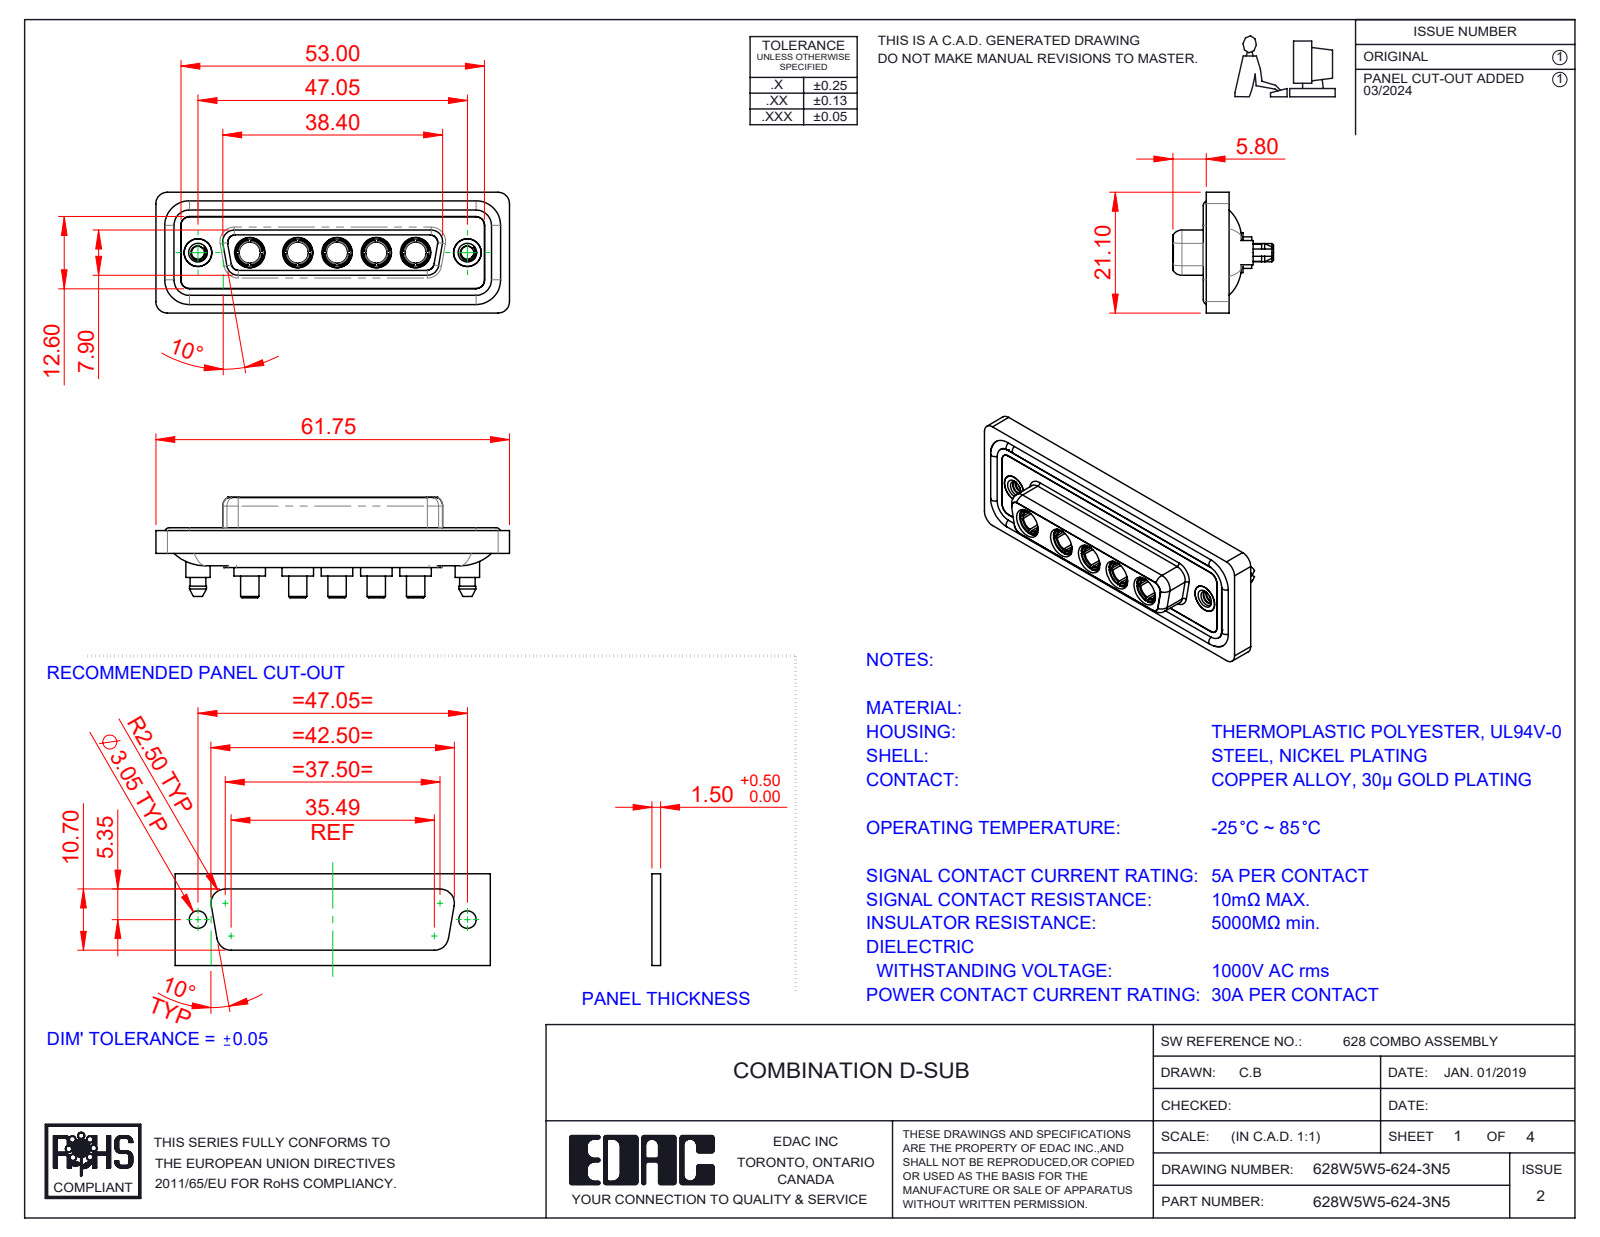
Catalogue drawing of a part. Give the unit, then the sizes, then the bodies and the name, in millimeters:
Units: millimetres
Overall size (bounding box): 61.75 × 21.1 × 17.55
Round holes (diameter × count): ⌀4.85 ×7, ⌀3.7 ×5, ⌀5.3 ×5, ⌀2.26 ×2, ⌀4 ×2, ⌀4.05 ×2, ⌀5 ×2
Round bosses / shafts (diameter × count): ⌀5.5 ×5, ⌀5.2 ×5, ⌀4.96 ×5, ⌀4.75 ×5, ⌀3.75 ×5, ⌀3.2 ×5, ⌀1.6 ×4, ⌀5.4 ×2
Partial cylindrical surfaces — rounded edges, fillets, slot ends (radius × count): R1.5 ×24, R2 ×18, R1.6 ×10, R1.35 ×8, R2.1 ×5, R0.25 ×4, R0.5 ×4, R0.6 ×4
Main face-to-face distances: 0.4, 1.8, 7.45, 5.65, 0.5, 7.05, 6.6, 1.6, 1.1, 2.9
Hole centre spacings: 6.86, 9.04, 13.72, 38.01, 8.39, 15.25, 15.9, 17.43
Volume: 8 342 mm³ · Surface area: 13 771 mm²
Bodies: 17 solids, 806 faces (266 planar, 335 cylindrical, 205 other)
Part name (STEP PRODUCT): 628W5W5-624-3N5; Power Socket_30A S; 628Combo Shell Rear_25 Contacts; 628Combo Waterproof Housing_25 Contacts (+3 more)
STEP written by: SolidWorks 2023 (CONFIG_CONTROL_DESIGN)
